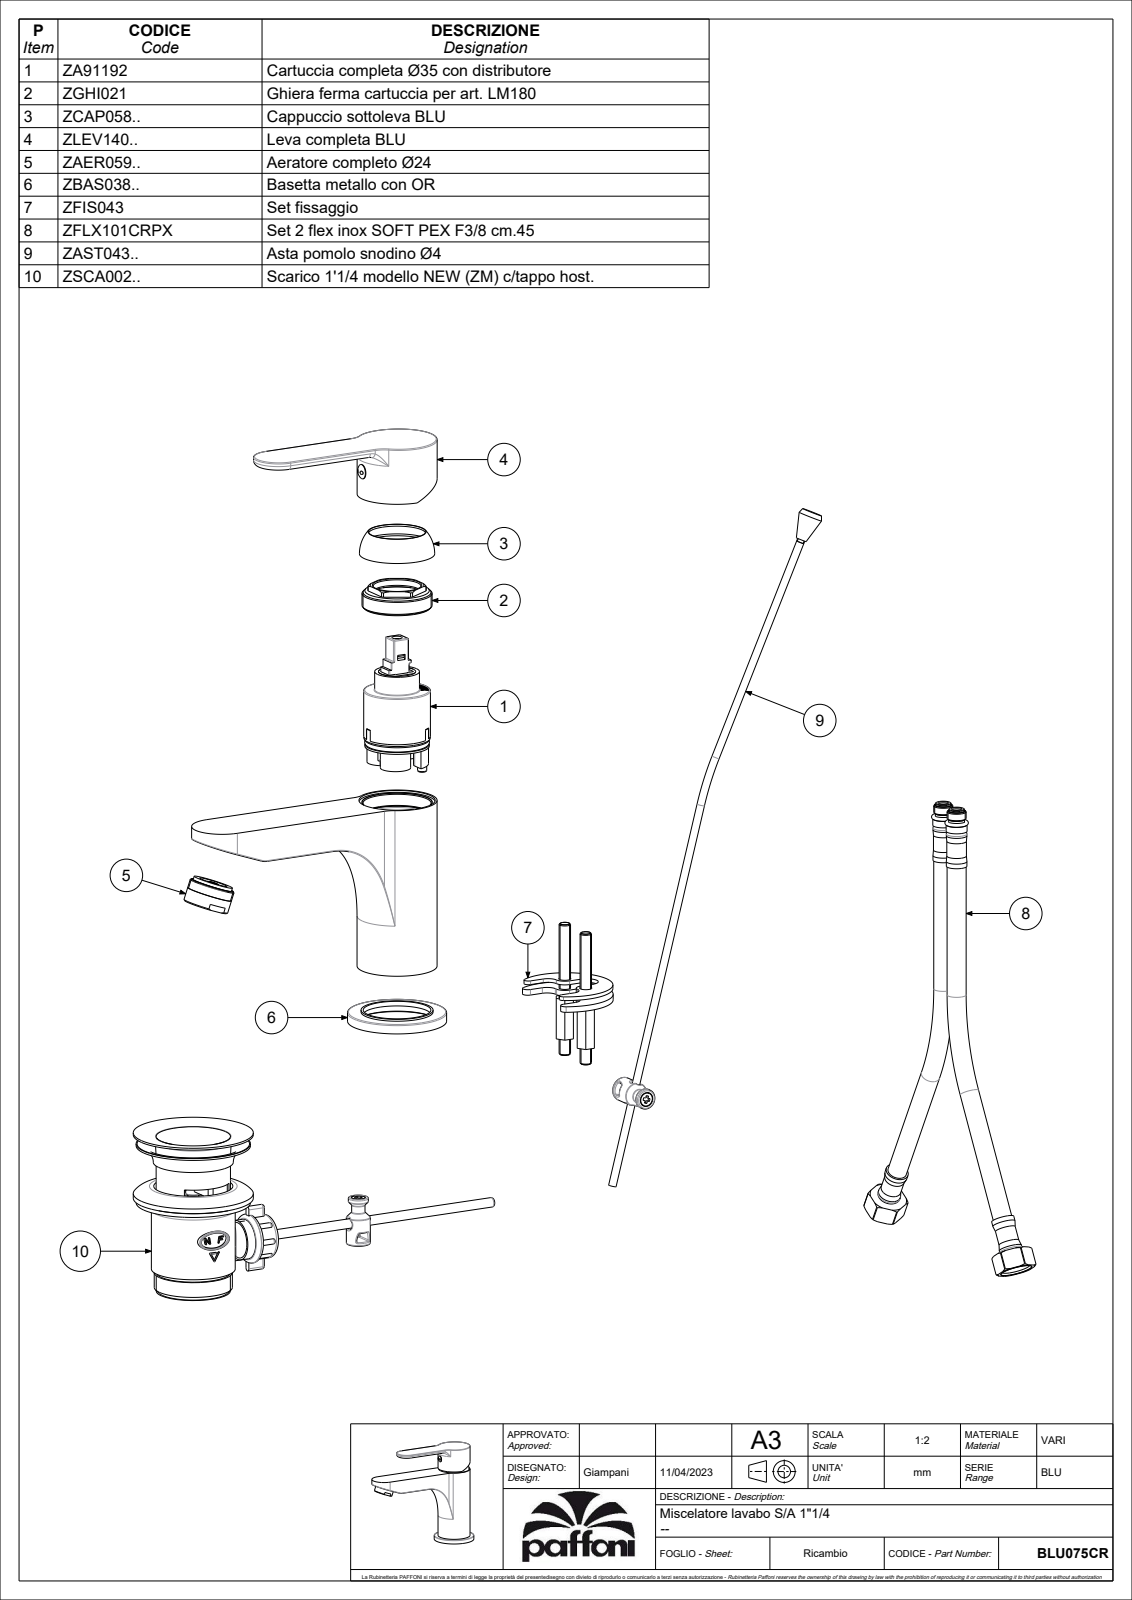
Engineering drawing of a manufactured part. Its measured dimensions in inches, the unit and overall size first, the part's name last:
Units: inches
Overall size (bounding box): 6.282 × 5.028 × 2.047
Round holes (diameter × count): ⌀0.197 ×4, ⌀0.354 ×3, ⌀0.472 ×3, ⌀0.236 ×2, ⌀0.256 ×2, ⌀0.315 ×2, ⌀0.118 ×1, ⌀0.13 ×1, ⌀0.138 ×1, ⌀0.157 ×1, ⌀0.181 ×1, ⌀0.217 ×1
Round bosses / shafts (diameter × count): ⌀0.551 ×2, ⌀0.472 ×2, ⌀0.433 ×2, ⌀0.413 ×2, ⌀0.394 ×2, ⌀0.236 ×2, ⌀0.197 ×2, ⌀0.189 ×2
Partial cylindrical surfaces — rounded edges, fillets, slot ends (radius × count): R0.02 ×70, R0.039 ×23, R0.012 ×20, R0.059 ×16, R0.021 ×14, R0.118 ×14, R0.047 ×9, R0.394 ×5
Main face-to-face distances: 0.118, 1.142, 1.26, 0.106, 0.039, 0.709, 1.024, 0.197, 3.748, 0.827
Hole centre spacings: 0.535, 0.028, 0.111, 0.335, 0.339, 0.38, 0.388, 0.44
Volume: 7.742 in³ · Surface area: 146.4 in²
Bodies: 3 solids, 2670 faces (1914 planar, 466 cylindrical, 290 other)
Part name (STEP PRODUCT): BLU075CR
STEP written by: CREO PARAMETRIC BY PTC INC, 2020044 (CONFIG_CONTROL_DESIGN)
